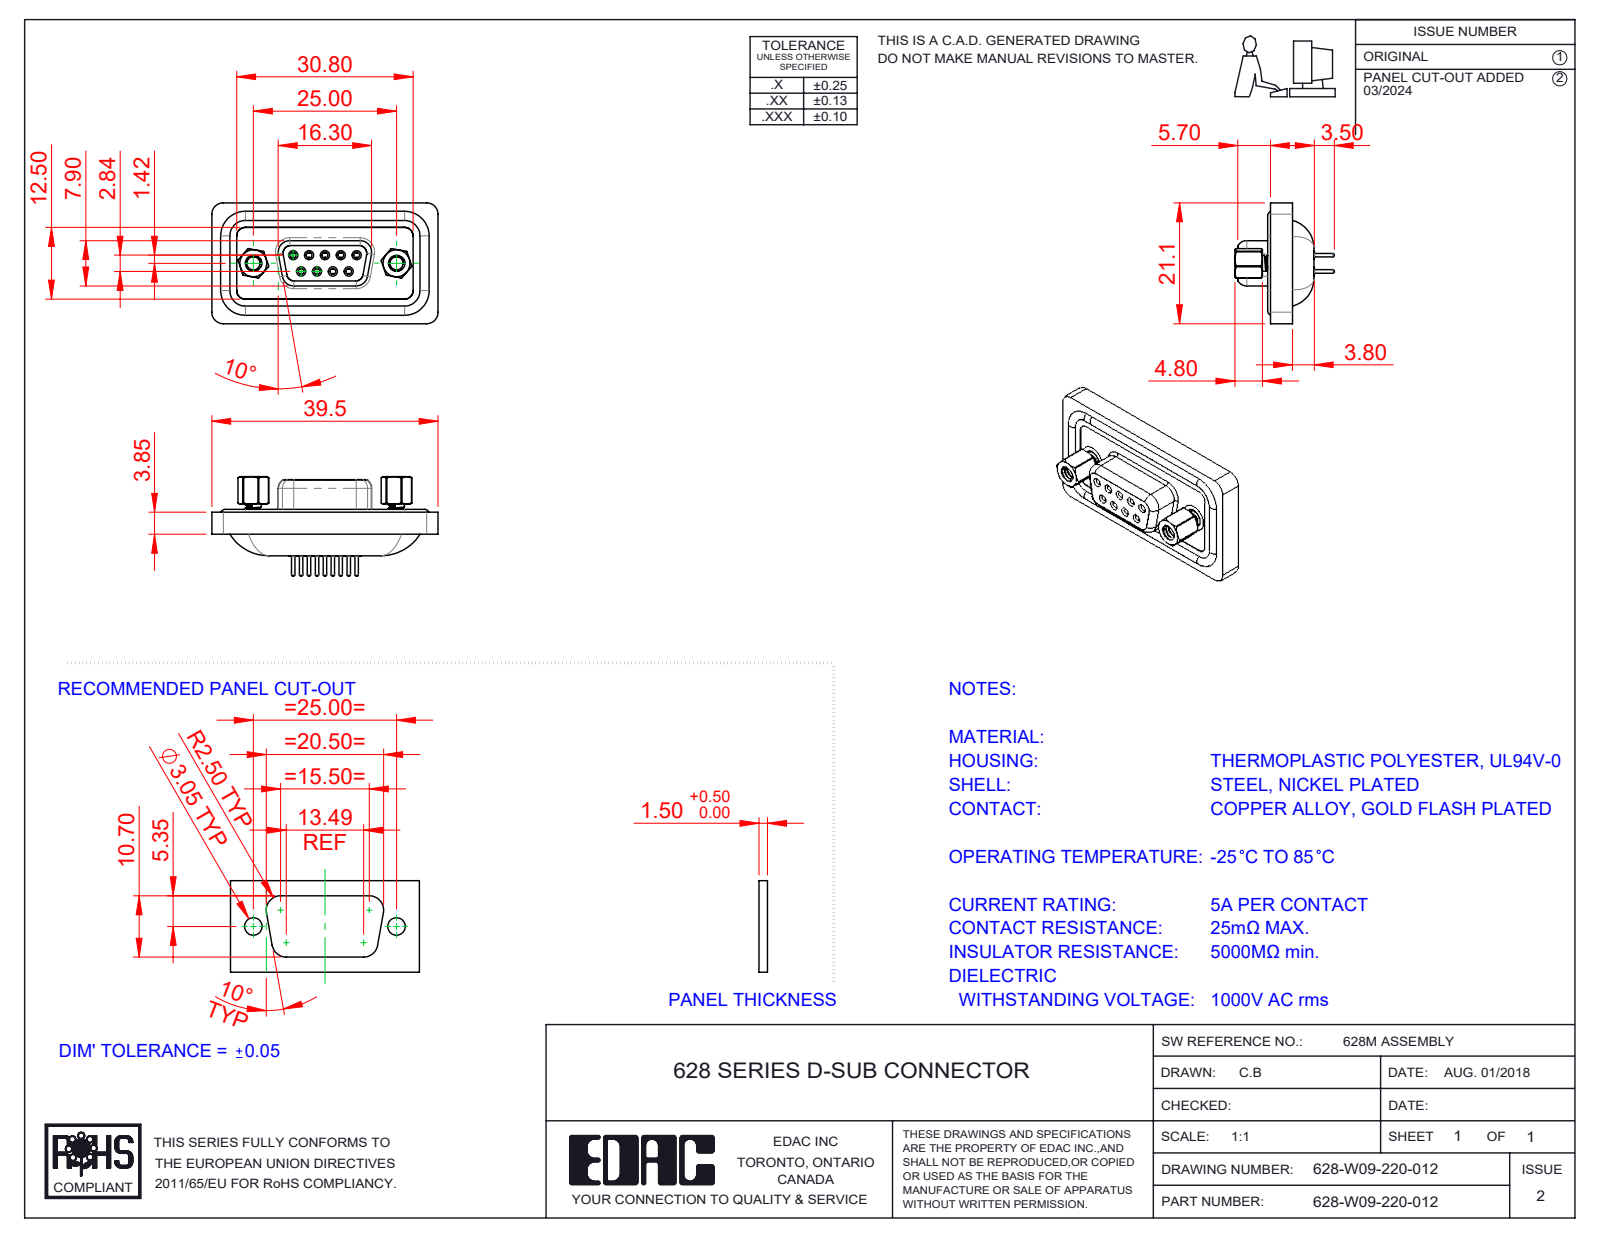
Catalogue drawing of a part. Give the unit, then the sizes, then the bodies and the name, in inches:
Units: inches
Overall size (bounding box): 1.555 × 0.831 × 0.663
Round holes (diameter × count): ⌀0.039 ×9, ⌀0.043 ×9, ⌀0.059 ×9, ⌀0.067 ×9, ⌀0.071 ×9, ⌀0.079 ×9, ⌀0.089 ×2, ⌀0.09 ×2, ⌀0.157 ×2, ⌀0.189 ×2, ⌀0.197 ×2
Round bosses / shafts (diameter × count): ⌀0.063 ×13, ⌀0.087 ×9, ⌀0.024 ×9, ⌀0.193 ×2, ⌀0.11 ×2
Partial cylindrical surfaces — rounded edges, fillets, slot ends (radius × count): R0.079 ×16, R0.059 ×14, R0.053 ×8, R0.106 ×6, R0.02 ×4, R0.035 ×4, R0.063 ×4, R0.069 ×4
Main face-to-face distances: 0.016, 0.043, 0.108, 0.02, 0.148, 0.039, 0.138, 0.132, 0.152, 0.295
Hole centre spacings: 0.124, 0.109, 0.218, 0.198, 0.198, 0.327, 0.28, 0.294
Volume: 0.307 in³ · Surface area: 11.5 in²
Bodies: 17 solids, 936 faces (236 planar, 409 cylindrical, 291 other)
Part name (STEP PRODUCT): 628-W09-220-012; 628W Housing_09 Contacts; 628W Contact Row 2_20; 628W Shell Front_09 Contacts (+4 more)
STEP written by: SolidWorks 2020 (CONFIG_CONTROL_DESIGN)
